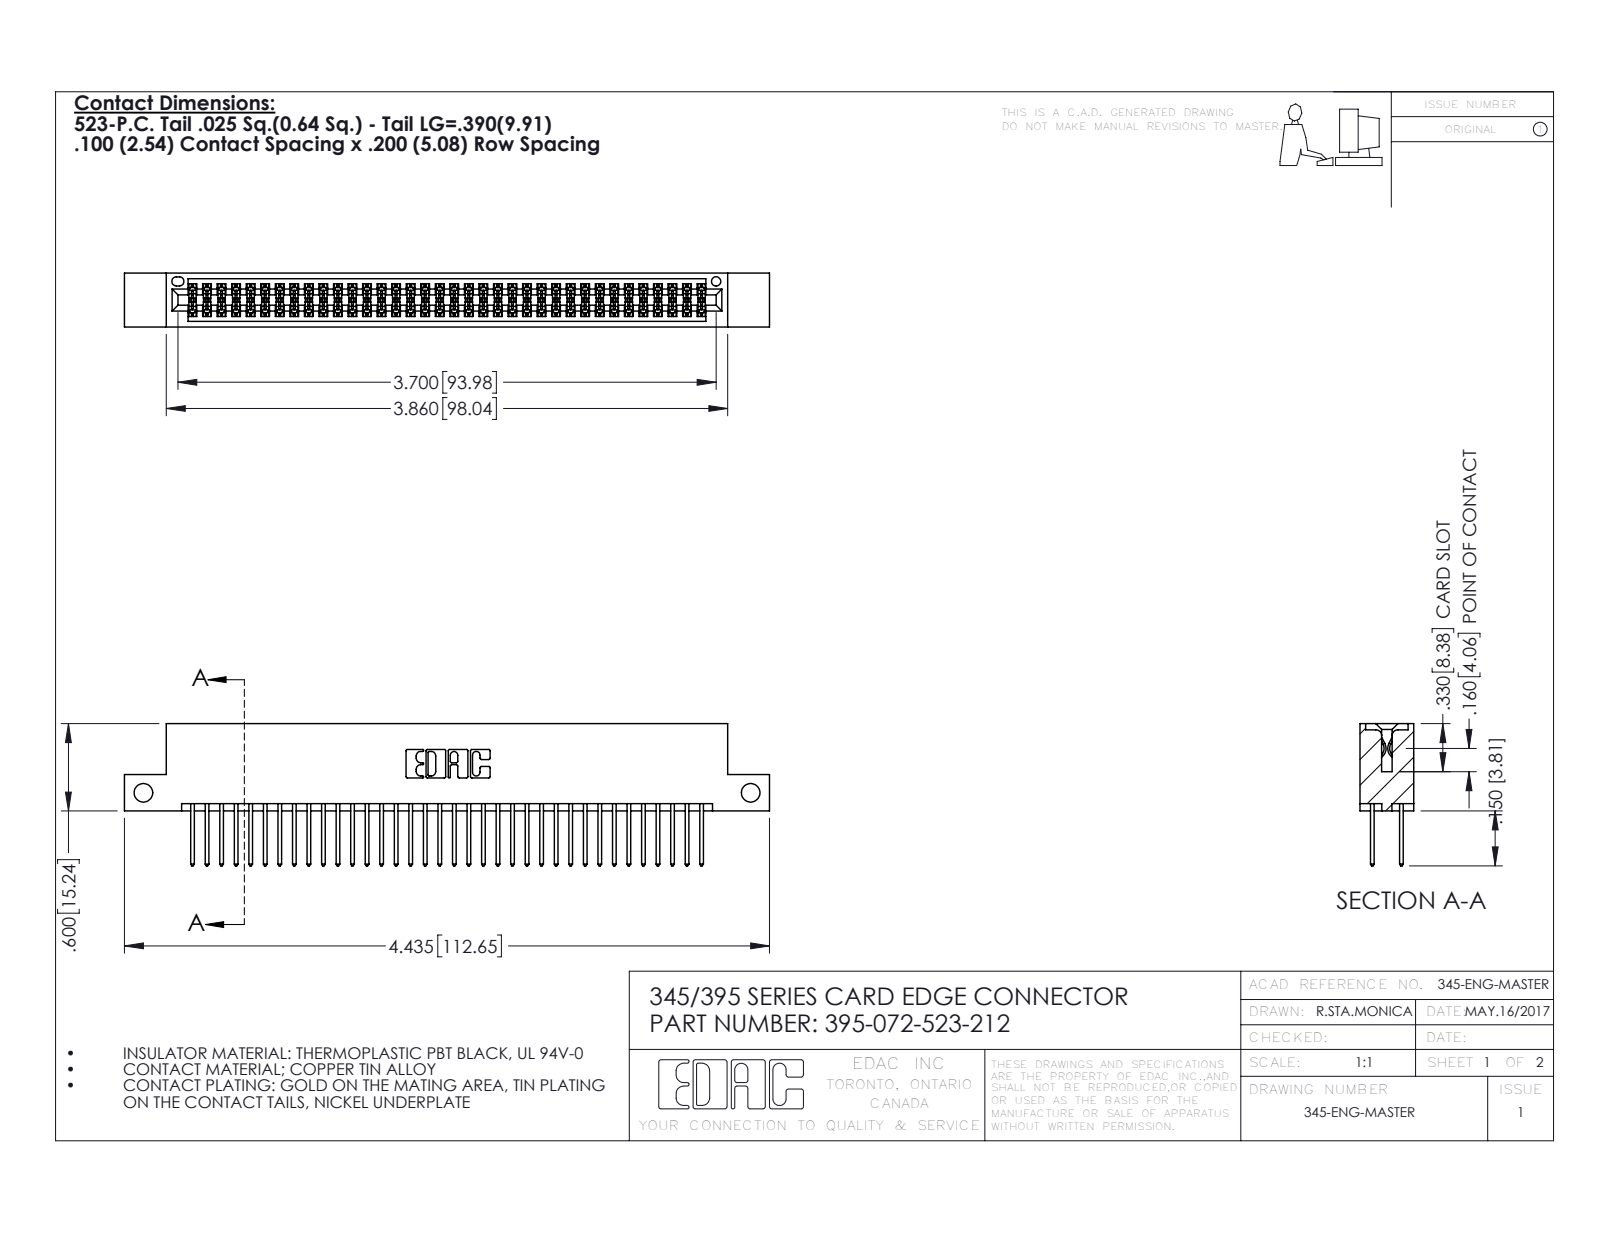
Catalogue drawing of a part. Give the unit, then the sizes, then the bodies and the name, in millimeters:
Units: millimetres
Overall size (bounding box): 112.6 × 24.8 × 9.4
Round holes (diameter × count): ⌀3.3 ×2, ⌀1.6 ×1
Partial cylindrical surfaces — rounded edges, fillets, slot ends (radius × count): R0.2 ×108, R0.3 ×72, R0.3 ×22, R0.2 ×6, R0.8 ×6, R0.7 ×3, R0.4 ×2, R0.5 ×2
Main face-to-face distances: 7.6, 1.8, 5.1, 2.5, 6.9, 0.6, 9.4, 5.7, 4.4, 3.8
Hole centre spacings: 106
Volume: 10 900 mm³ · Surface area: 16 590 mm²
Bodies: 73 solids, 3726 faces (2456 planar, 1270 cylindrical, 0 other)
Part name (STEP PRODUCT): 345 Part_Flush Mounting Lugs - Side Mount; 345-292-001_345-293-123; 395-072-523-212
STEP written by: SolidWorks 2016 (CONFIG_CONTROL_DESIGN)
